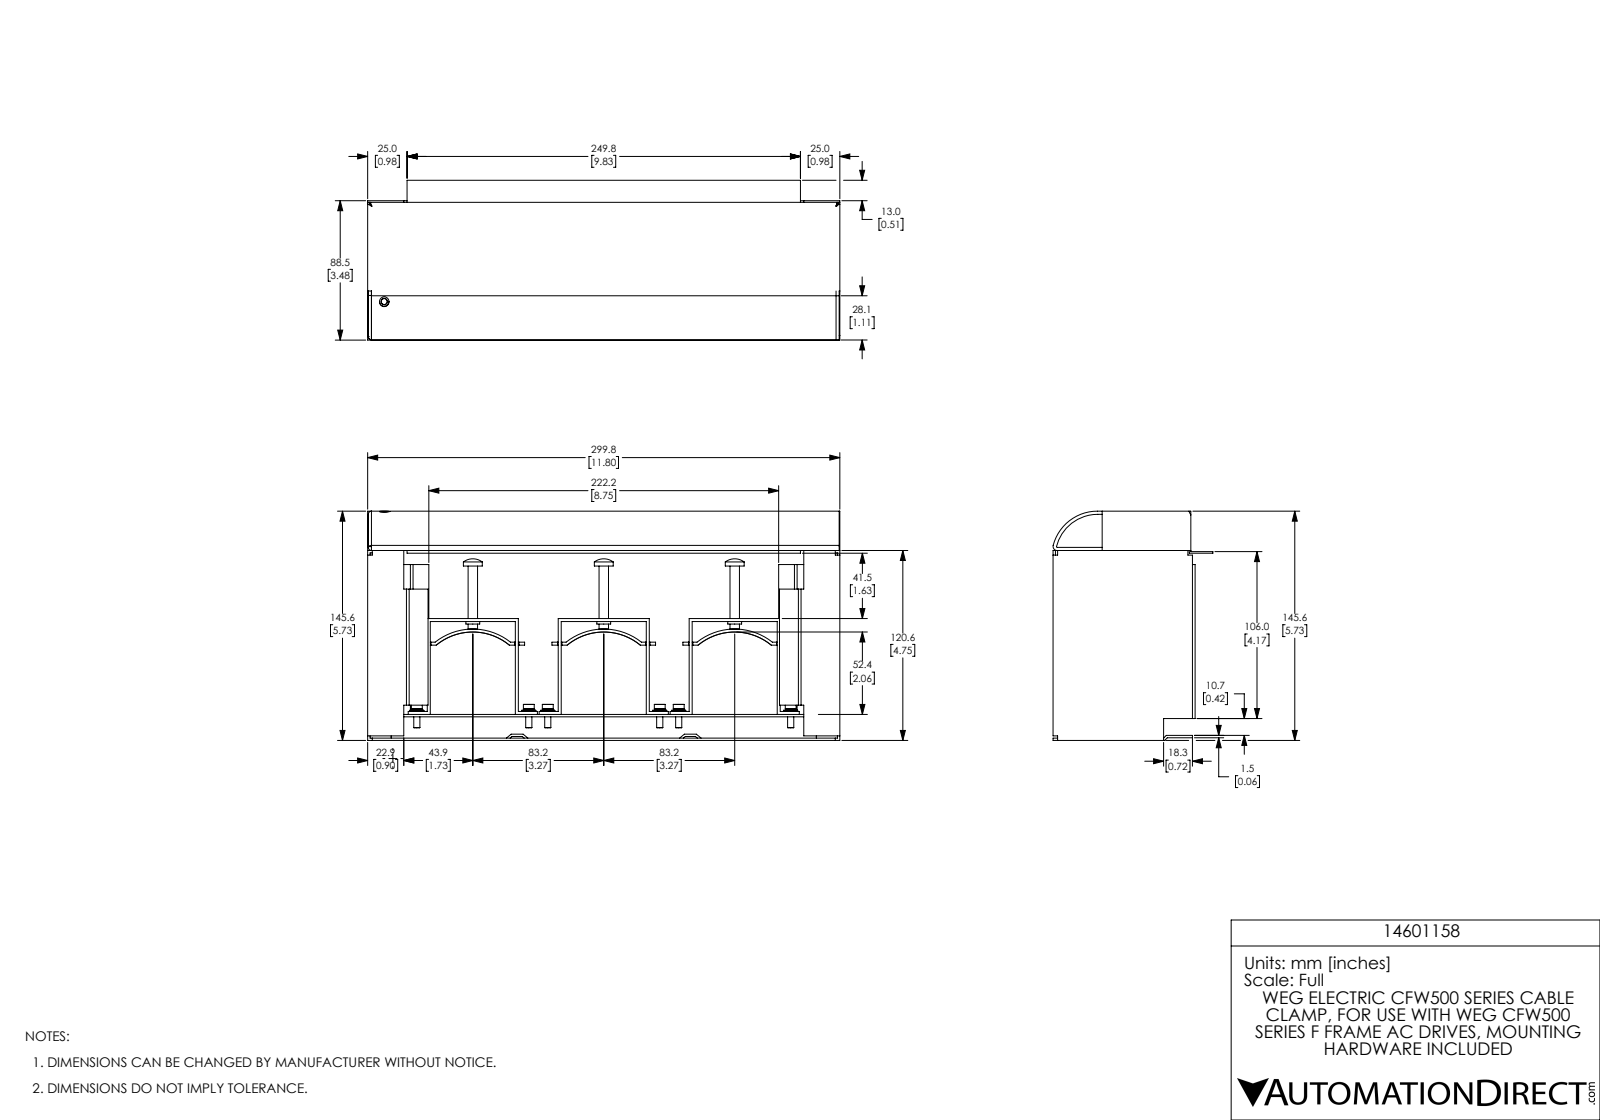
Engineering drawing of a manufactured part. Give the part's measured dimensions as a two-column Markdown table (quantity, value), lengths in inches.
| quantity | value |
| --- | --- |
| part name | 14601158_CONJ BLINDAGEM CABOS CFW500_KPCSF R1 NC ext1 |
| STEP written by | SolidWorks 2017 (AUTOMOTIVE_DESIGN) |
| units | inches |
| bodies | 20 solids, 725 faces (456 planar, 128 cylindrical, 141 other) |
| overall size | 11.803 × 5.732 × 3.996 |
| volume | 12.91 in³ |
| surface area | 458.7 in² |
| round holes (diameter × count) | 0.228 × 6, 0.098 × 1 |
| round bosses / shafts (diameter × count) | 0.35 × 6, 0.272 × 6, 0.26 × 6, 0.248 × 6, 0.154 × 6, 0.13 × 6, 0.472 × 3, 0.346 × 3 |
| partial cylindrical surfaces (radius × count) | 0.079 × 4, 1.435 × 3, 1.51 × 3, 0.043 × 2, 1.102 × 2, 0.063 × 1, 0.102 × 1, 1.142 × 1 |
| main face-to-face distances | 0.059, 0.039, 0.067, 11.744, 5.732, 5.673, 5.693, 5.634, 0.591, 0.945 |
| hole center spacings | 3.274, 2.799, 0.474, 6.073, 6.547, 1.567, 3.748, 3.854 |
